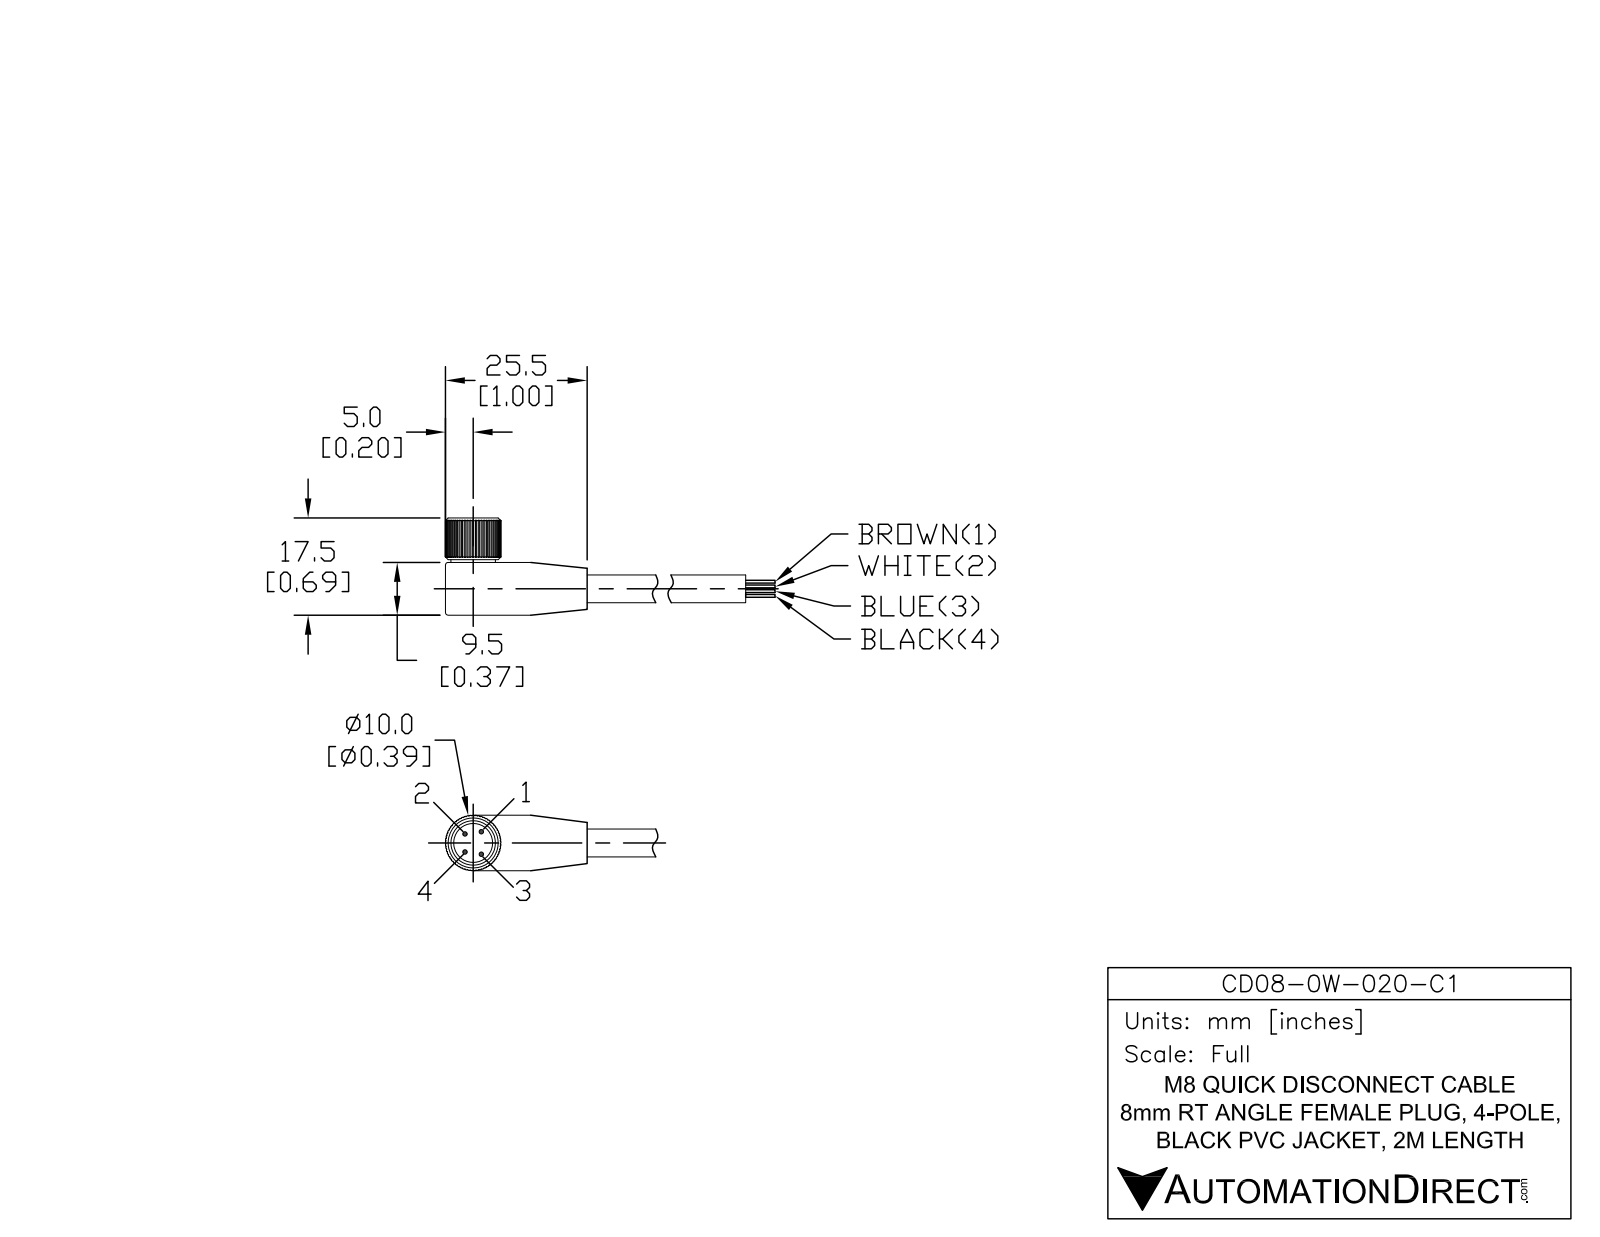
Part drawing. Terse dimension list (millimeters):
name: CD08-0W-020-C1
written by: SolidWorks 2017 (AUTOMOTIVE_DESIGN)
unit: mm
bodies: 4 solids, 306 faces (220 planar, 83 cylindrical, 3 other)
size: 128.6 × 19.1 × 10
volume: 4 341 mm³; area: 3 353 mm²
holes: 4× ⌀0.9, 1× ⌀7.2, 1× ⌀8
bosses: 2× ⌀10, 1× ⌀7, 1× ⌀6.6, 1× ⌀4.8
rounds: 1× R4.9
face distances: 7.7, 0.6, 9, 7.1, 100, 4.6, 3.1, 4, 2.5, 5.2
hole spacings: 2.19, 2.5, 3.03, 4.69, 3.2, 4
